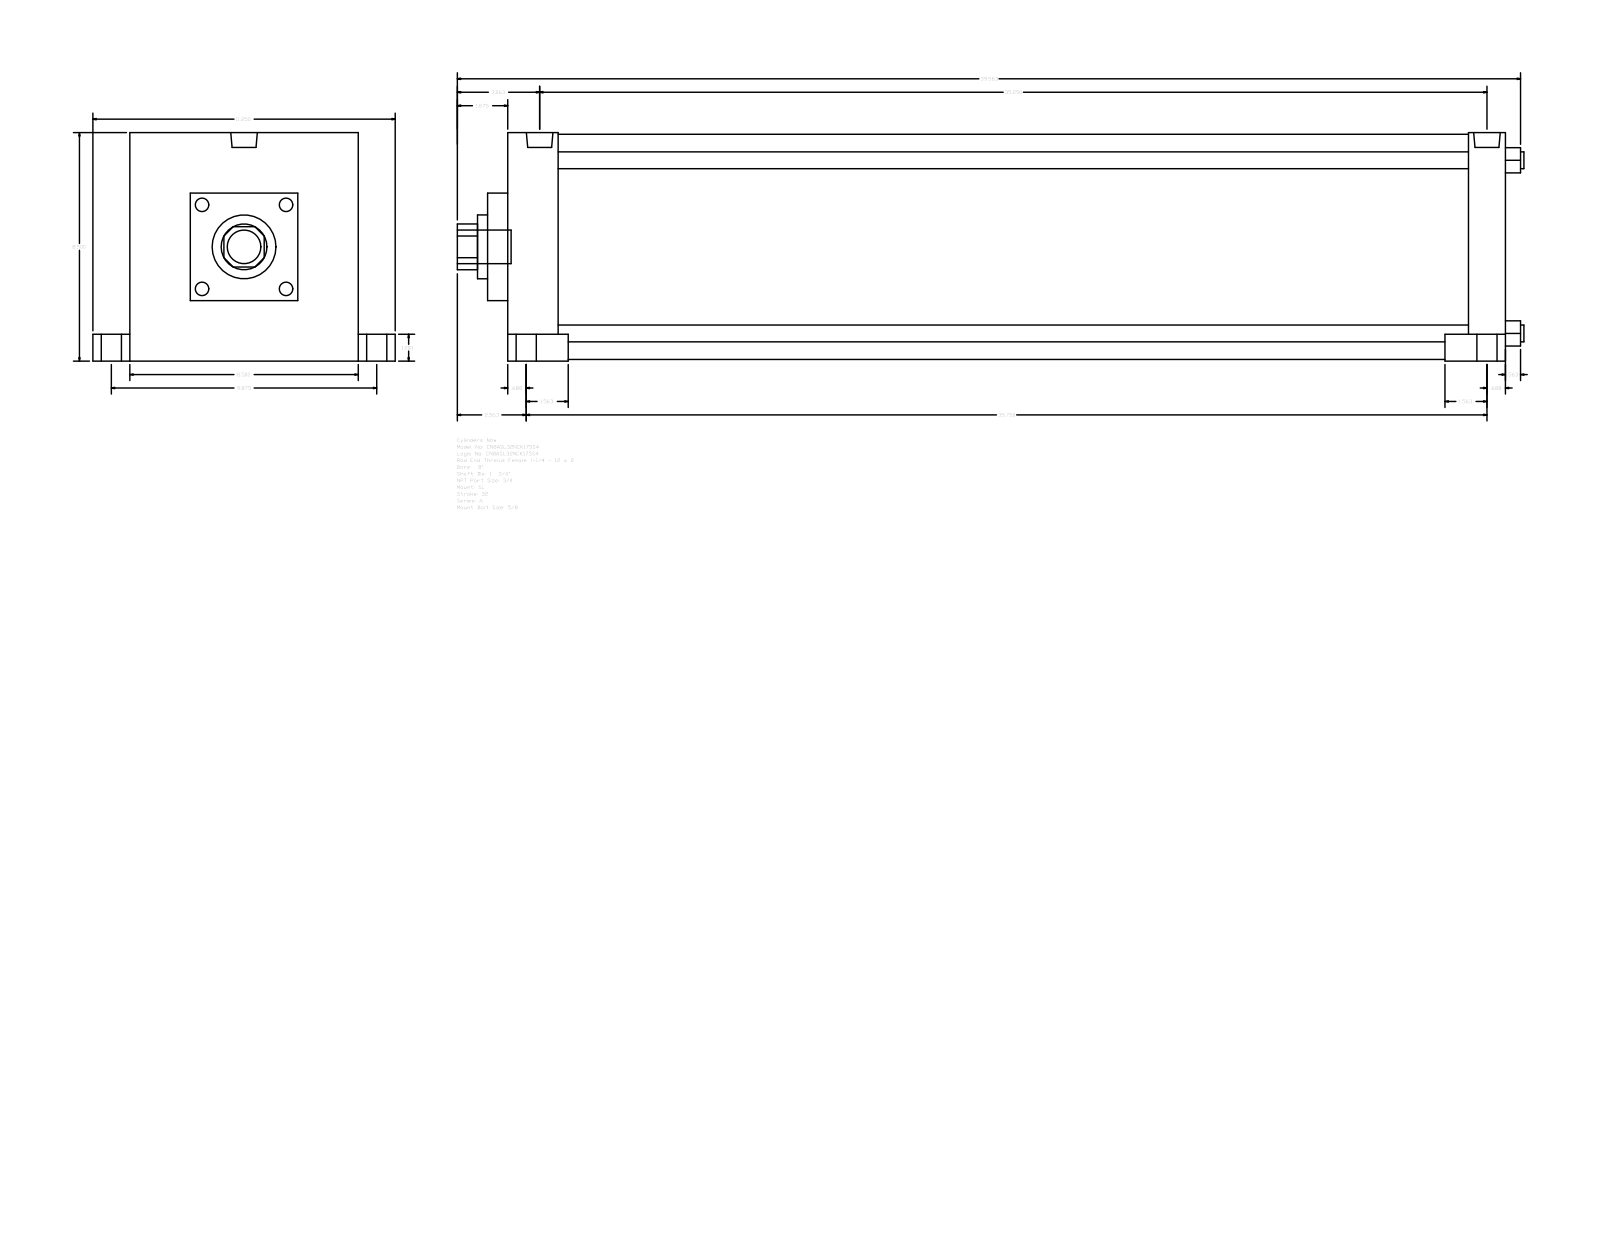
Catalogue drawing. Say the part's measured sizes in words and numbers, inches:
The part is named "A_SL__0800_1.75". Its 3-D file was written by "GSSL Pune (CONFIG_CONTROL_DESIGN)". It is 0 solids with 117 faces: 85 planar, 32 cylindrical and 0 other. Overall it measures 39.687 by 11.25 by 8.5 inches. Round holes: 4 of diameter 0.625, 1 of diameter 1.75, 1 of diameter 2.375, 1 of diameter 8.375. Round bosses or shafts: 4 of diameter 1, 4 of diameter 0.75, 4 of diameter 0.594, 2 of diameter 0.989, 1 of diameter 1.25. Partial cylindrical surfaces (rounded edges, fillets, slot ends): 1 of radius 0.852. The main face-to-face distances are 37.125, 8.5, 1.375, 1.875, 35.25, 35.75, 33.875, 2.25, 0.75, 6.25. The hole center spacings are 4.554, 6.44, 9.108.
